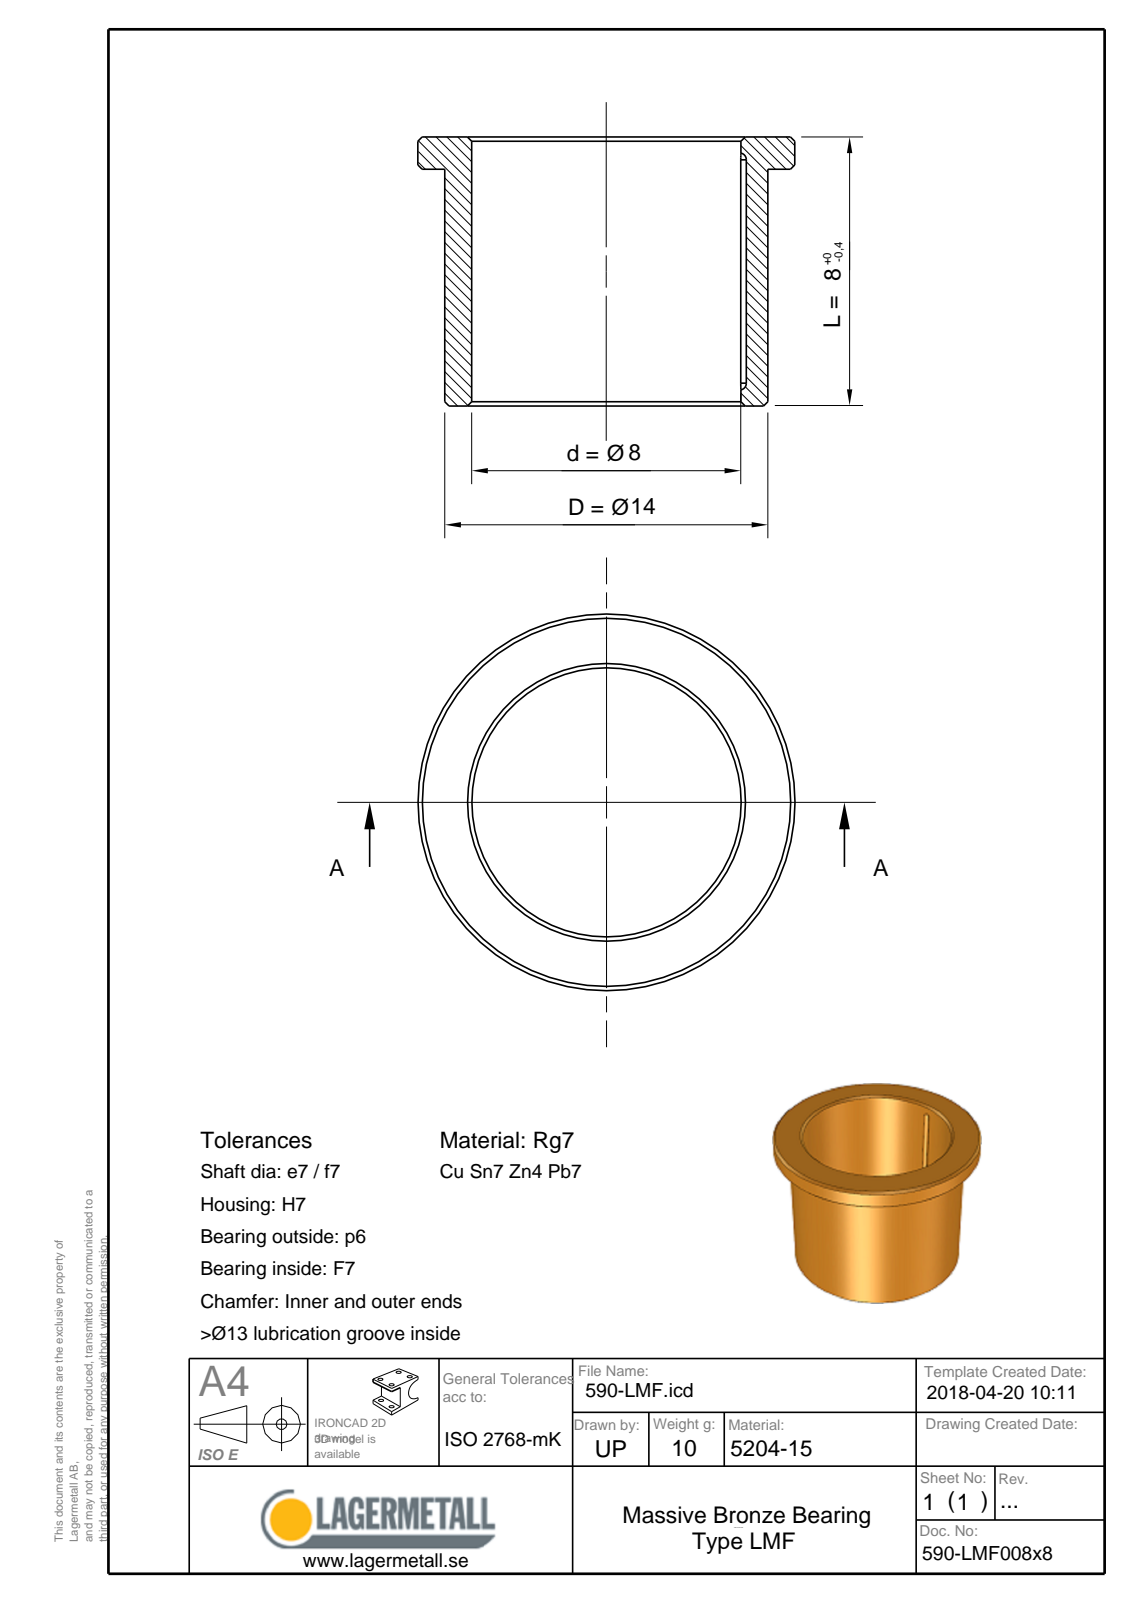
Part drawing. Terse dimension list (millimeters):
name: 590-LMF008x8
written by: Spatial InterOp 3D (CONFIG_CONTROL_DESIGN)
unit: mm
bodies: 1 solid, 11 faces (3 planar, 3 cylindrical, 5 other)
size: 18 × 18 × 8
volume: 1 122 mm³; area: 962 mm²
holes: 1× ⌀8
bosses: 1× ⌀18, 1× ⌀14
face distances: 3, 5, 8
